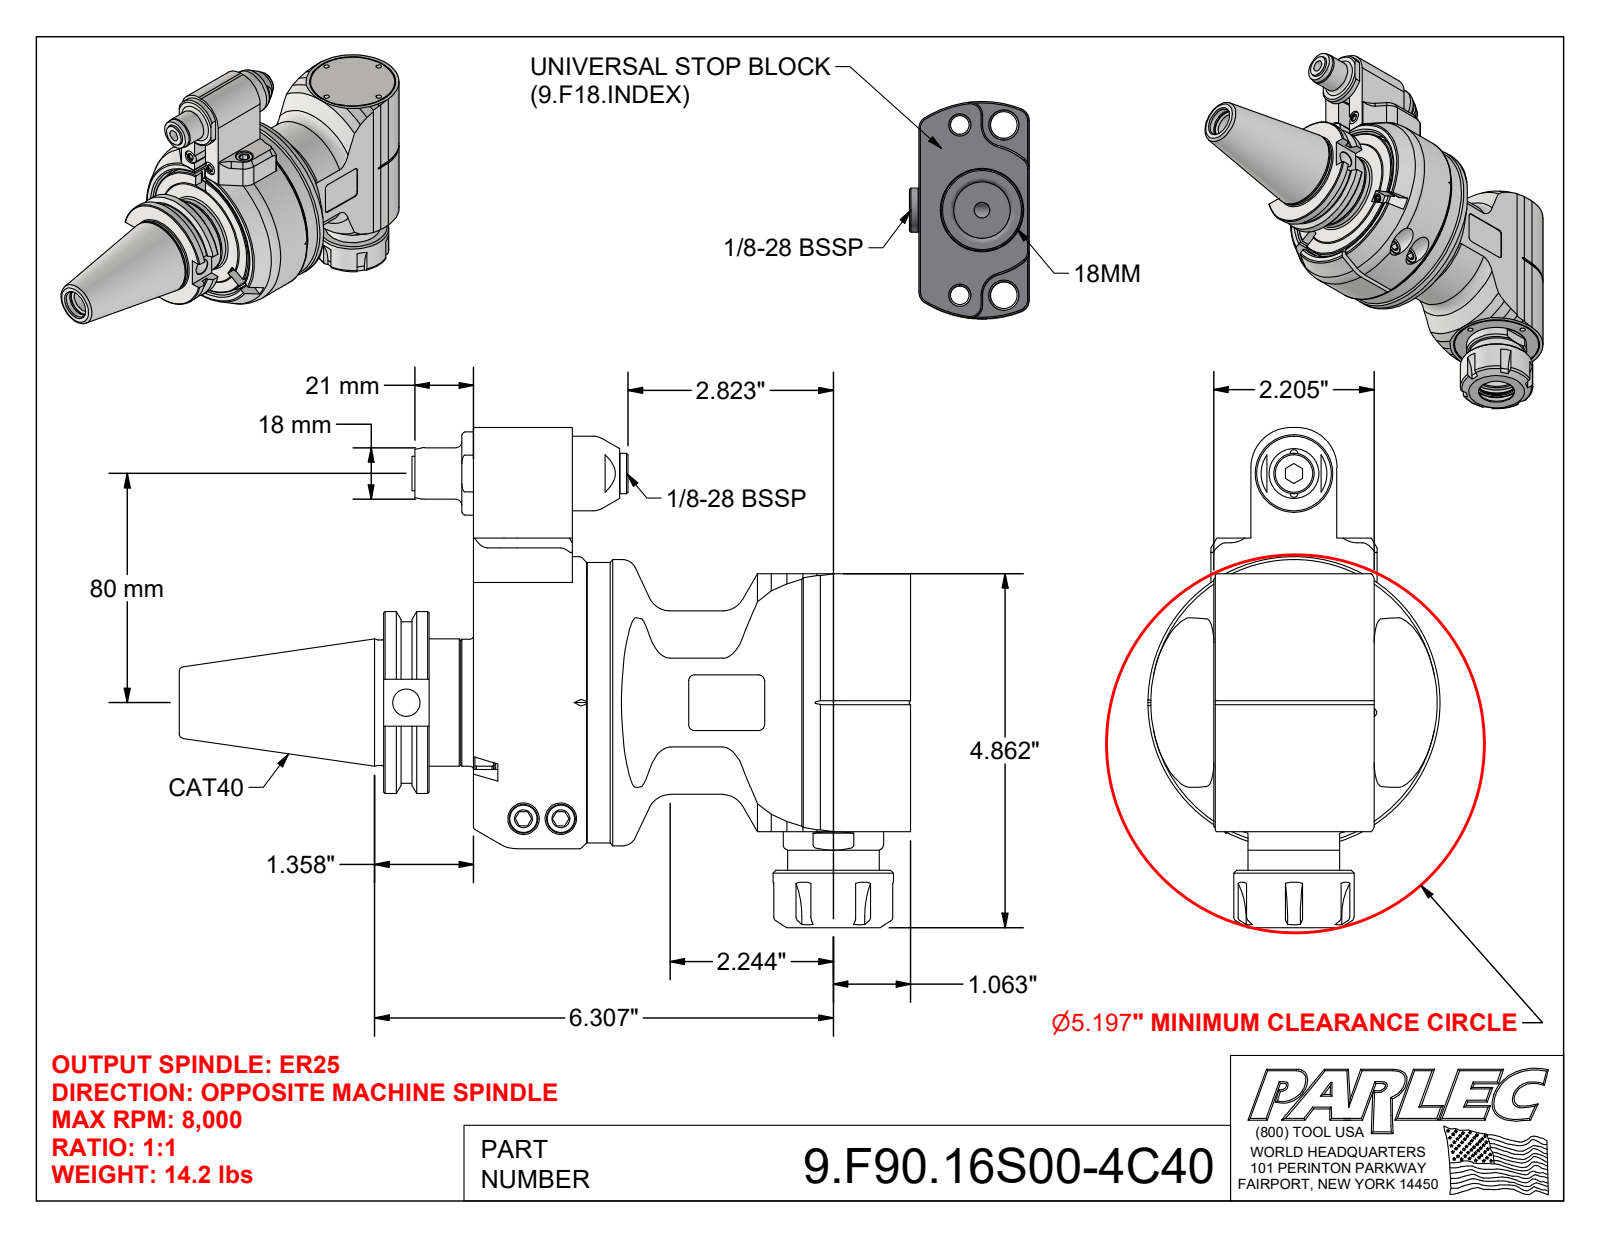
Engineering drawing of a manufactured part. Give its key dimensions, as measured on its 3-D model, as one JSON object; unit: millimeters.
{"part_name": "9.F90.16S00-4C40; 9_GA1_448_2 (Type 1, Cat40, 80mm); 9_F90_16S00", "step_written_by": "Autodesk Inventor 2022 (AUTOMOTIVE_DESIGN)", "units": "millimeters", "bodies": {"solids": 26, "faces": 788, "planar": 321, "cylindrical": 217, "other": 250}, "overall_size": [255.4, 174.5, 102], "volume_mm3": 1003000, "surface_area_mm2": 175000, "round_holes": [[3.2, 8], [5, 7], [4.2, 6], [3.3, 4], [6, 3], [6.5, 3], [8, 3], [2.6, 2], [6.8, 2], [10.4, 2], [11, 2], [12.5, 2]], "round_bosses_or_shafts": [[10, 5], [6, 4], [4, 4], [22, 2], [18, 2], [12, 2], [5, 2], [2.5, 2]], "partial_cylinders_radius": [[1, 14], [2, 12], [3, 6], [25, 6], [4, 4], [0.4, 2], [0.5, 2], [8, 2]], "face_to_face_distances": [3, 32, 0.5, 7, 31.8, 39.5, 16.5, 7.7, 8.5, 32.5], "hole_center_spacings": [8.3, 11.7, 21.5, 30.4, 7, 12, 16.5, 21.3]}
